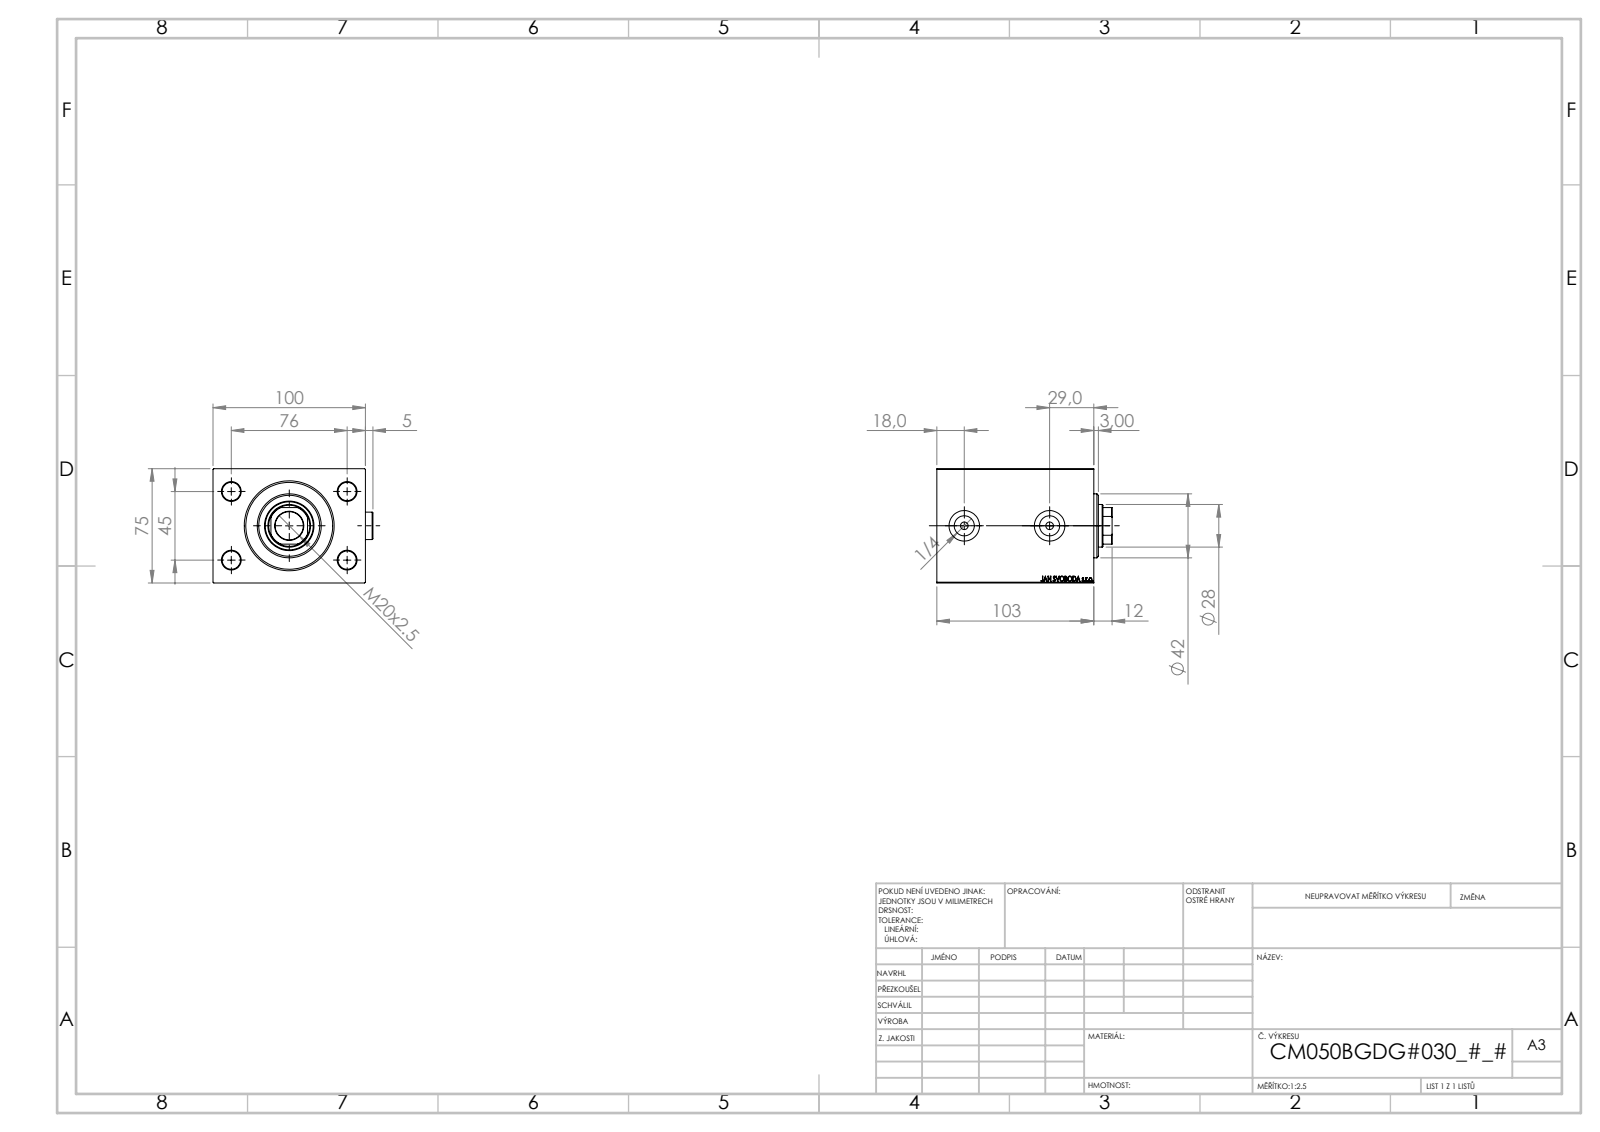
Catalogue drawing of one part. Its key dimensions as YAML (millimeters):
part_name: "V450CM_VC_B; V450CM_B_Body; V450CM_B_VCP; Zatka_OIL_PORT"
step_written_by: "SolidWorks 2019 (CONFIG_CONTROL_DESIGN)"
units: millimeters
bodies: {solids: 5, faces: 938, planar: 436, cylindrical: 72, other: 430}
overall_size: [115, 104.9, 75]
volume: 708440
surface_area: 100692
round_holes:
  - {diameter: 12, count: 4}
  - {diameter: 5, count: 2}
  - {diameter: 13.16, count: 2}
  - {diameter: 20, count: 2}
  - {diameter: 18.5, count: 1}
  - {diameter: 28, count: 1}
  - {diameter: 31.5, count: 1}
  - {diameter: 32.5, count: 1}
  - {diameter: 50, count: 1}
  - {diameter: 52, count: 1}
  - {diameter: 57, count: 1}
round_bosses_or_shafts:
  - {diameter: 18, count: 2}
  - {diameter: 42, count: 1}
partial_cylinders:
  - {radius: 13.5, count: 1}
face_to_face_distances: [75, 100, 103, 14, 89, 12, 77, 91, 61, 42]
hole_center_spacings: [44.16, 45, 76, 88.32, 56]
